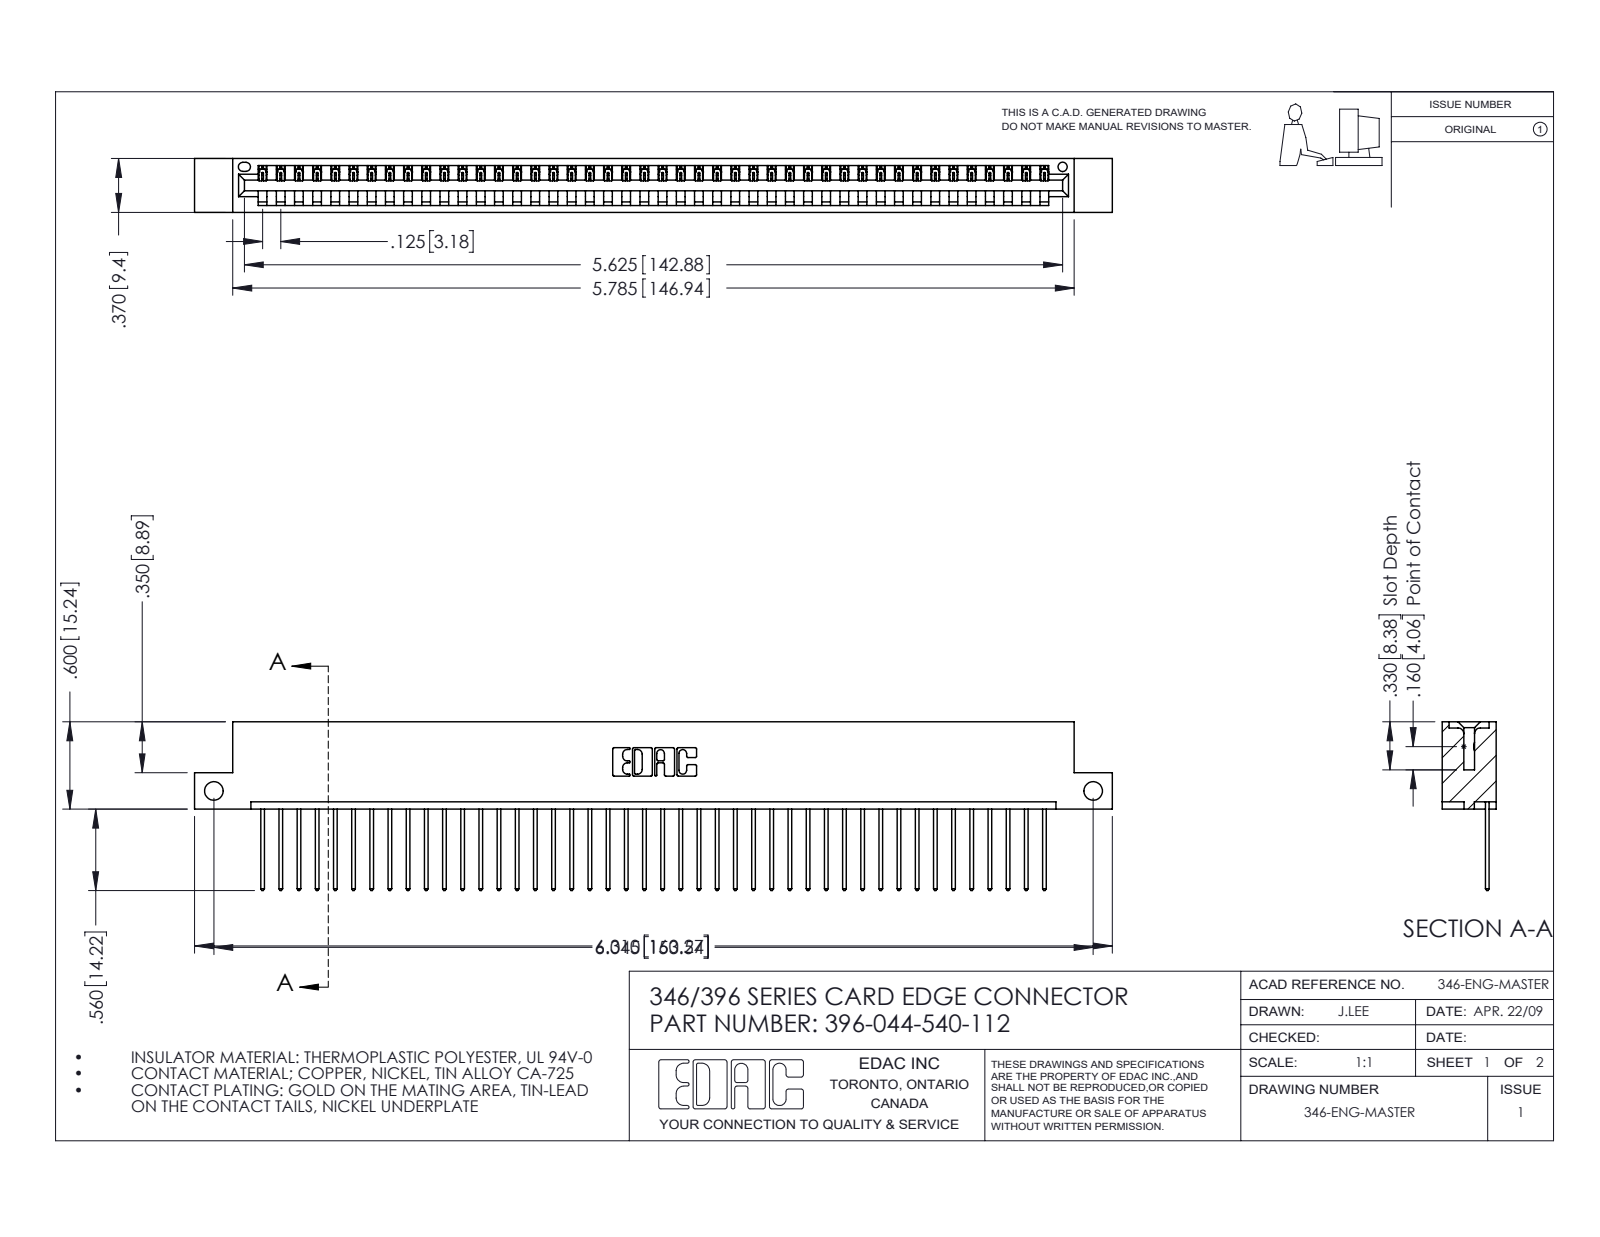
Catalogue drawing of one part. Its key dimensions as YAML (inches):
part_name: "345-292-001_345-293-140; 346 Part_Flush Mounting Lugs - Side Mount; 396-044-540-112"
step_written_by: "SolidWorks 2016 (CONFIG_CONTROL_DESIGN)"
units: inches
bodies: {solids: 45, faces: 2674, planar: 1836, cylindrical: 838, other: 0}
overall_size: [6.31, 1.16, 0.37]
volume: 0.935
surface_area: 30.18
round_holes:
  - {diameter: 0.128, count: 2}
  - {diameter: 0.064, count: 1}
partial_cylinders:
  - {radius: 0.006, count: 88}
  - {radius: 0.01, count: 88}
  - {radius: 0.01, count: 22}
  - {radius: 0.007, count: 6}
  - {radius: 0.031, count: 6}
  - {radius: 0.026, count: 3}
  - {radius: 0.031, count: 2}
  - {radius: 0.04, count: 2}
face_to_face_distances: [0.048, 0.322, 0.37, 0.25, 0.072, 0.298, 0.025, 0.148, 0.222, 0.1]
hole_center_spacings: [6.045]
